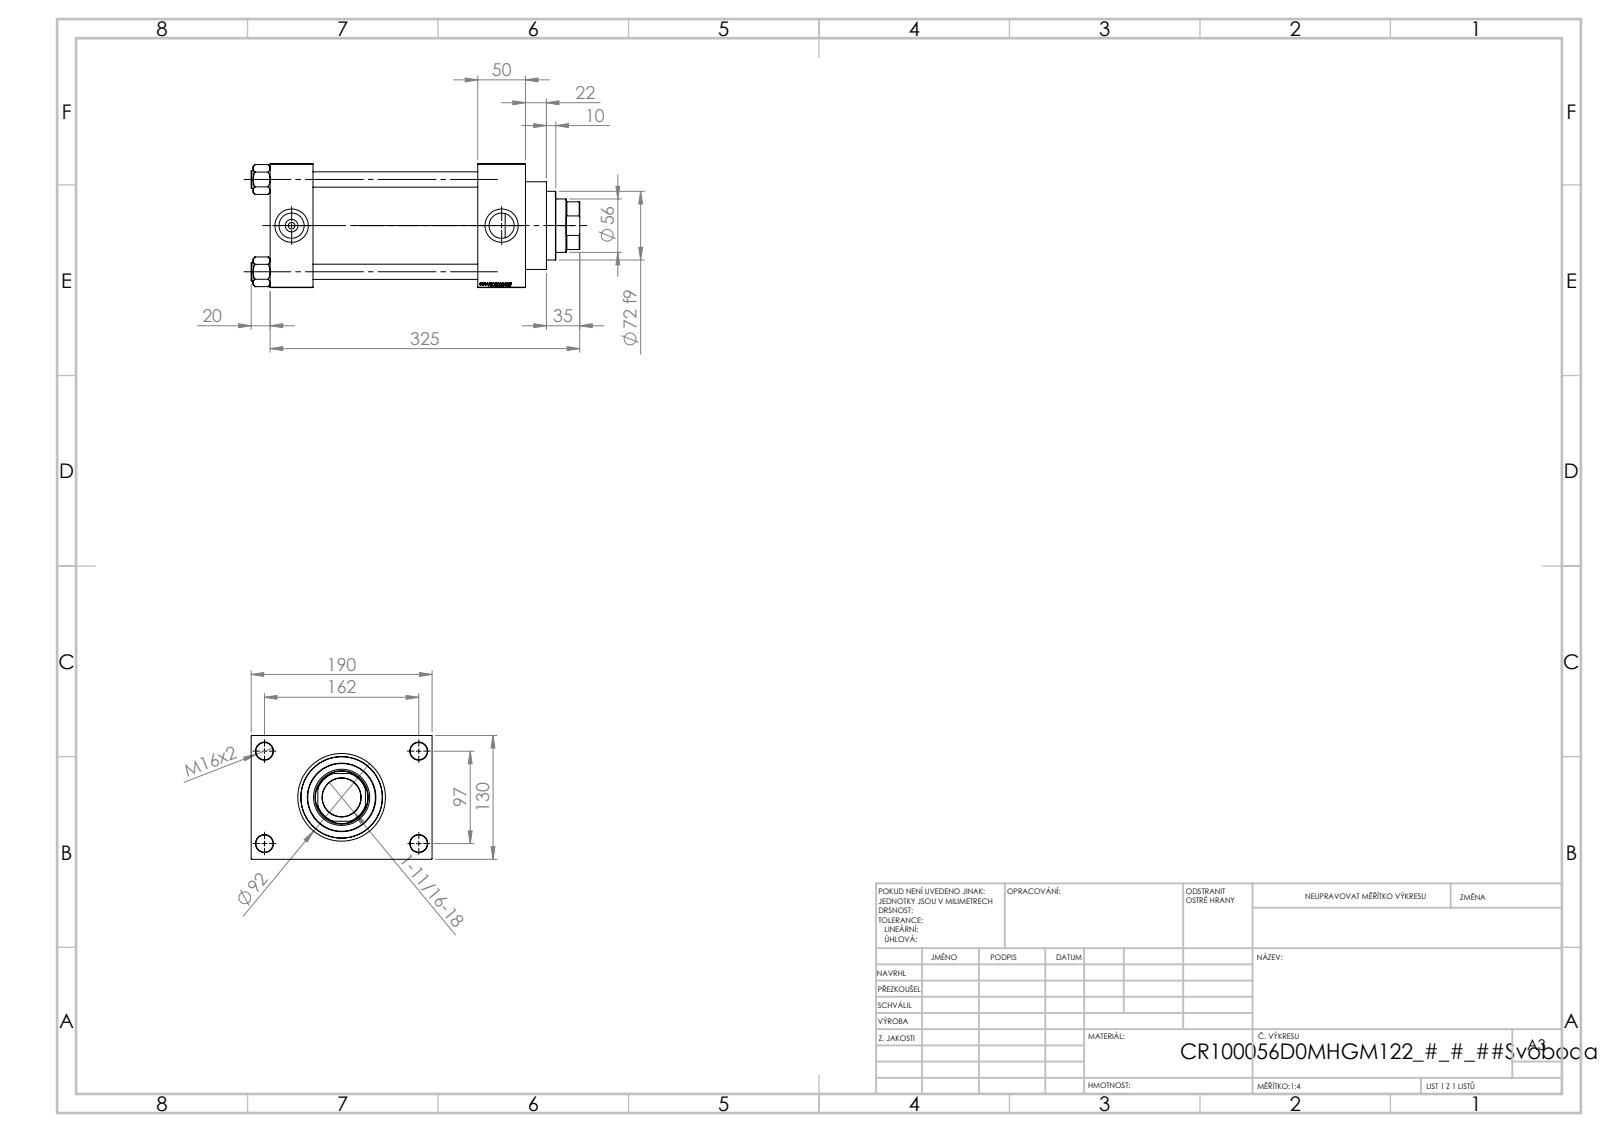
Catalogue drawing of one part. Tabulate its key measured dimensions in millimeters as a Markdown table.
| quantity | value |
| --- | --- |
| part name | NUT_M5_D; V215CR_D_Body; V215CR_VCP_D; V215_VC_A (+1 more) |
| STEP written by | SolidWorks 2019 (CONFIG_CONTROL_DESIGN) |
| units | millimeters |
| bodies | 11 solids, 1151 faces (545 planar, 88 cylindrical, 518 other) |
| overall size | 345 × 190 × 130 |
| volume | 3 060 000 mm³ |
| surface area | 466 827 mm² |
| round holes (diameter × count) | 16 × 4, 18 × 4, 7 × 2, 26.44 × 2, 35 × 2, 40.5 × 1, 56 × 1, 59 × 1, 76 × 1, 85.5 × 1, 100 × 1 |
| round bosses / shafts (diameter × count) | 19 × 4, 106 × 1, 92 × 1, 72 × 1 |
| partial cylindrical surfaces (radius × count) | 27 × 1 |
| main face-to-face distances | 130, 50, 45, 218, 173, 268, 223, 30, 160, 190 |
| hole center spacings | 32.55, 68.52, 94.41, 96.9, 102.27, 129.45, 161.73, 97 |
